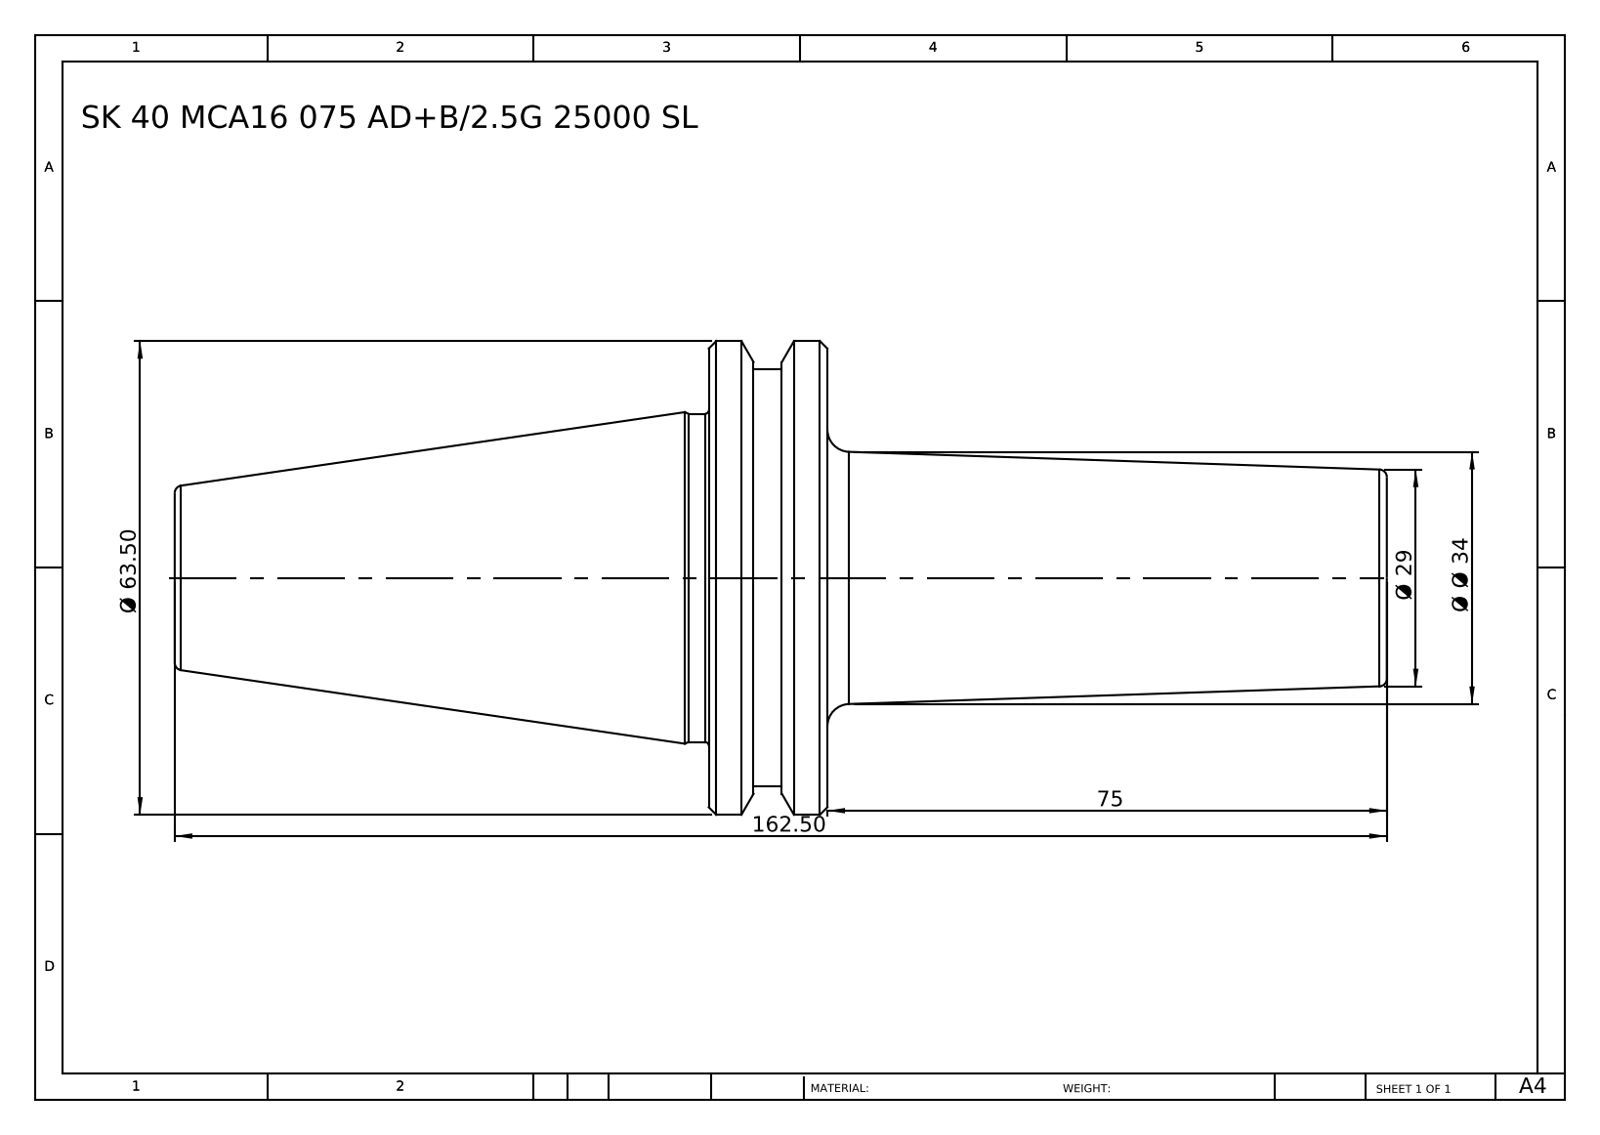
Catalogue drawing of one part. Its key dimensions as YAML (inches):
part_name: "SK 40 MCA16 075 AD+B-2.5G 25000 SL"
step_written_by: "SolidWorks 2014 (CONFIG_CONTROL_DESIGN)"
units: inches
bodies: {solids: 1, faces: 36, planar: 6, cylindrical: 8, other: 22}
overall_size: [6.398, 2.5, 2.5]
volume: 10.73
surface_area: 37.14
round_bosses_or_shafts:
  - {diameter: 2.5, count: 1}
  - {diameter: 2.205, count: 1}
  - {diameter: 1.732, count: 1}
face_to_face_distances: [0.626, 2.953, 3.579, 6.398, 3.445, 2.819, 3.193, 0.24, 0.386, 3.205]
